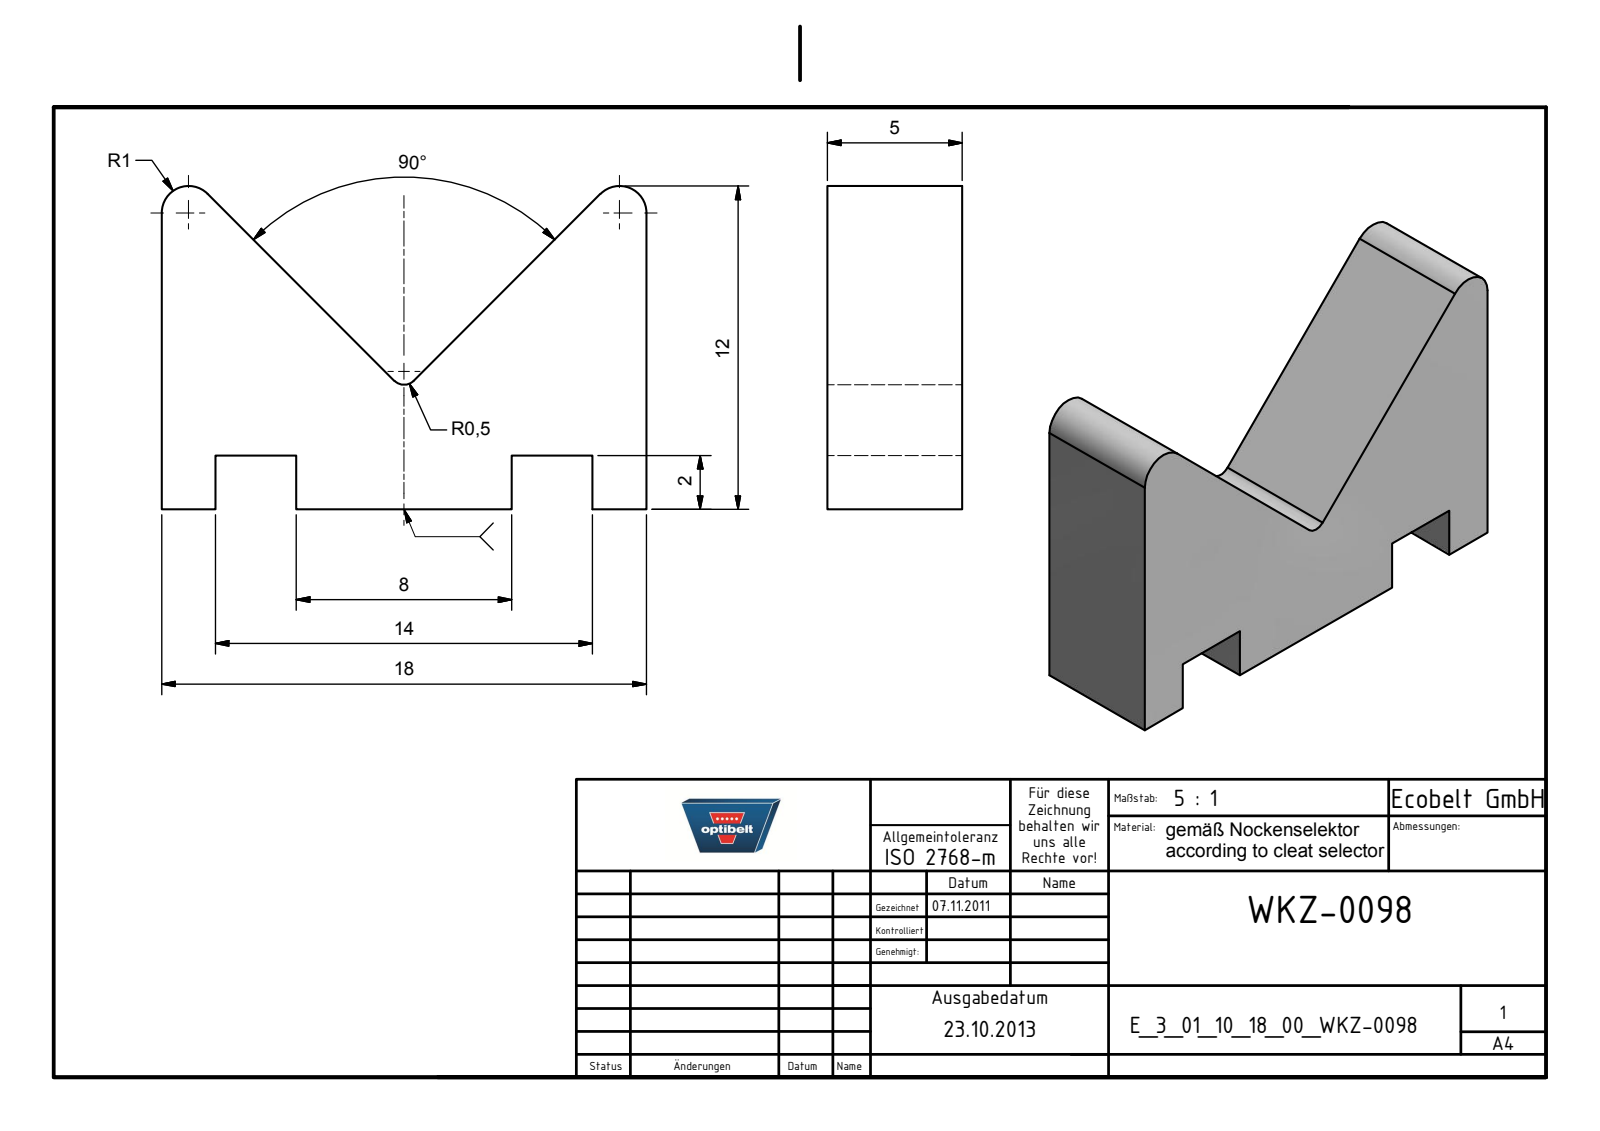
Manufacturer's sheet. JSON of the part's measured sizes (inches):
{"part_name": "E_3_01_10_18_00_WKZ-0098", "step_written_by": "Autodesk Inventor 2025 (AUTOMOTIVE_DESIGN)", "units": "inches", "bodies": {"solids": 1, "faces": 18, "planar": 15, "cylindrical": 3, "other": 0}, "overall_size": [0.709, 0.472, 0.197], "volume_in3": 0.045, "surface_area_in2": 1.02, "partial_cylinders_radius": [[0.039, 2], [0.02, 1]], "face_to_face_distances": [0.197, 0.709, 0.079, 0.512, 0.63, 0.118, 0.433, 0.551, 0.315]}
